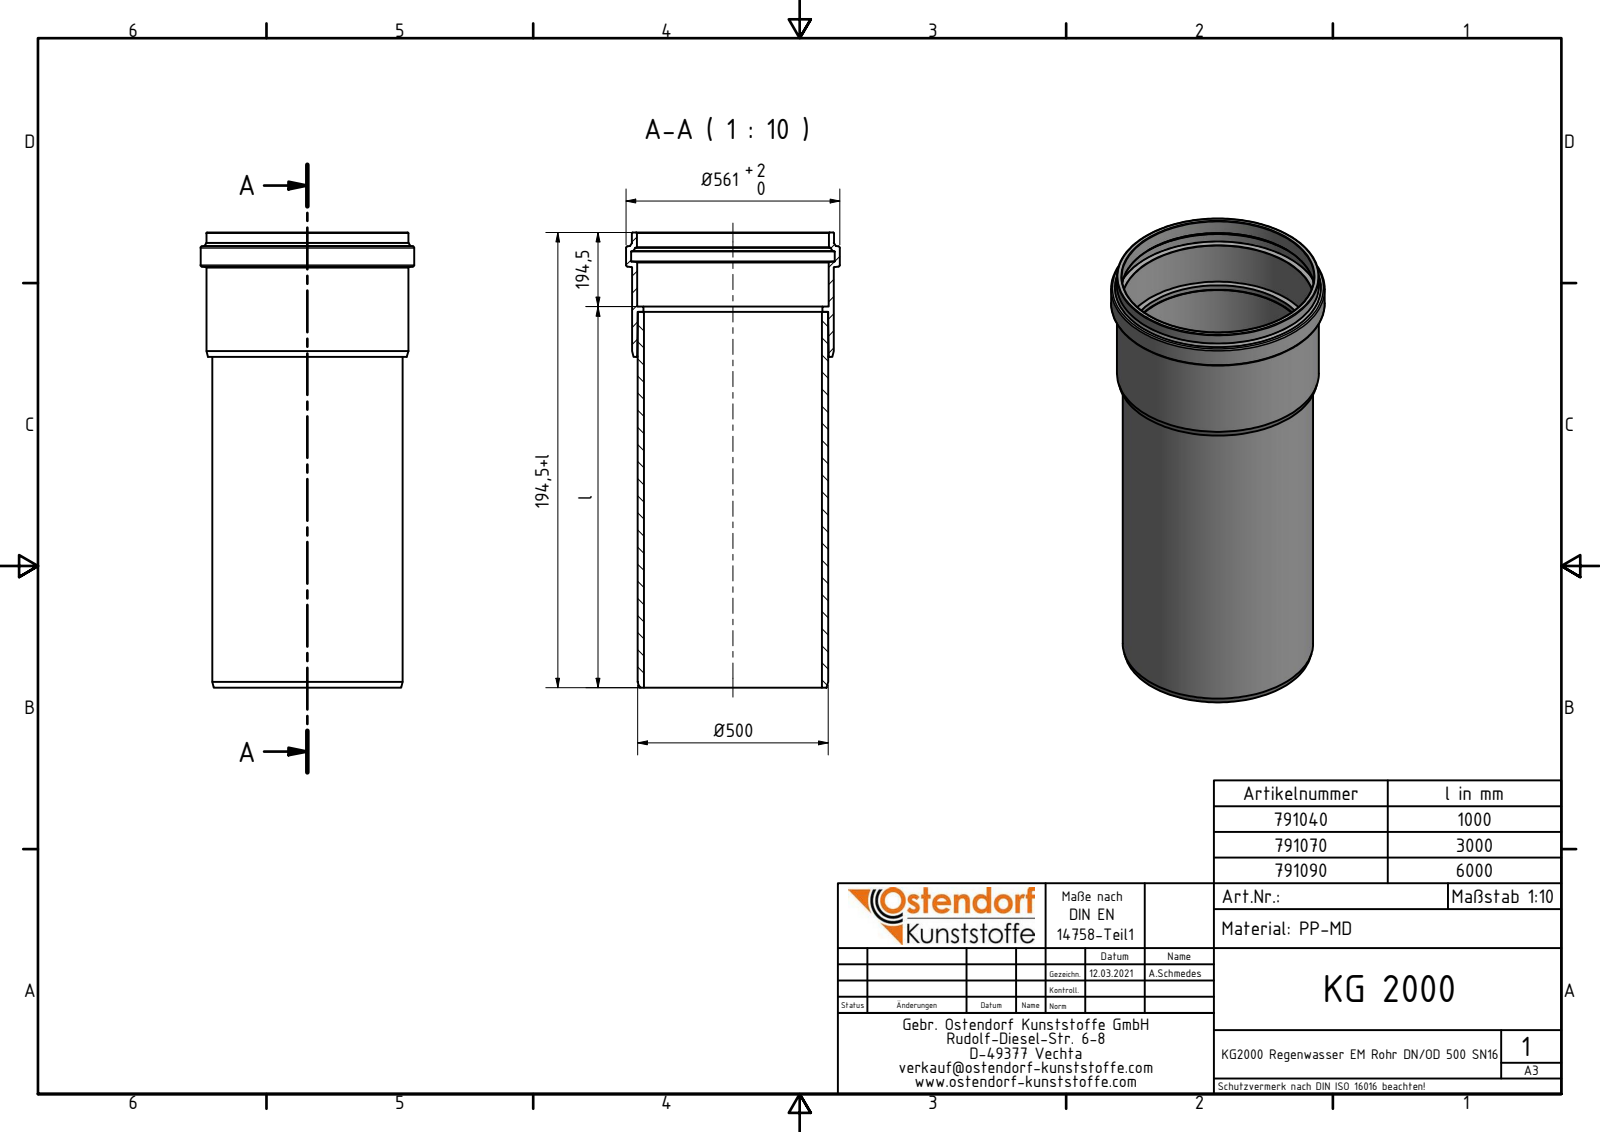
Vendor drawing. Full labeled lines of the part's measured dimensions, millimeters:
Part name (STEP PRODUCT): 791040 KG2000EM Rohr-Passlängen Regenwasser DN_OD 500x1000 SN16 Zusammanbau; 791040 KG2000EM Rohr-Passlängen Regenwasser DN_OD 500x1000 Teil1 SN16; 791040 KG2000EM Rohr-Passlängen Regenwasser DN_OD 500x1000 Teil2 SN16
STEP written by: Autodesk Inventor 2020 (AUTOMOTIVE_DESIGN)
Units: millimetres
Bodies: 2 solids, 39 faces (6 planar, 9 cylindrical, 24 other)
Overall size (bounding box): 1194.5 × 561 × 561
Volume: 32 830 000 mm³ · Surface area: 4 261 000 mm²
Round holes (diameter × count): ⌀467 ×1, ⌀470 ×1, ⌀503.5 ×1, ⌀504.5 ×1, ⌀535 ×1
Round bosses / shafts (diameter × count): ⌀561 ×1, ⌀530.5 ×1, ⌀530 ×1, ⌀500 ×1
Main face-to-face distances: 14, 1000, 986, 194.5, 208.5, 1194.5, 326.5, 132, 118, 868
